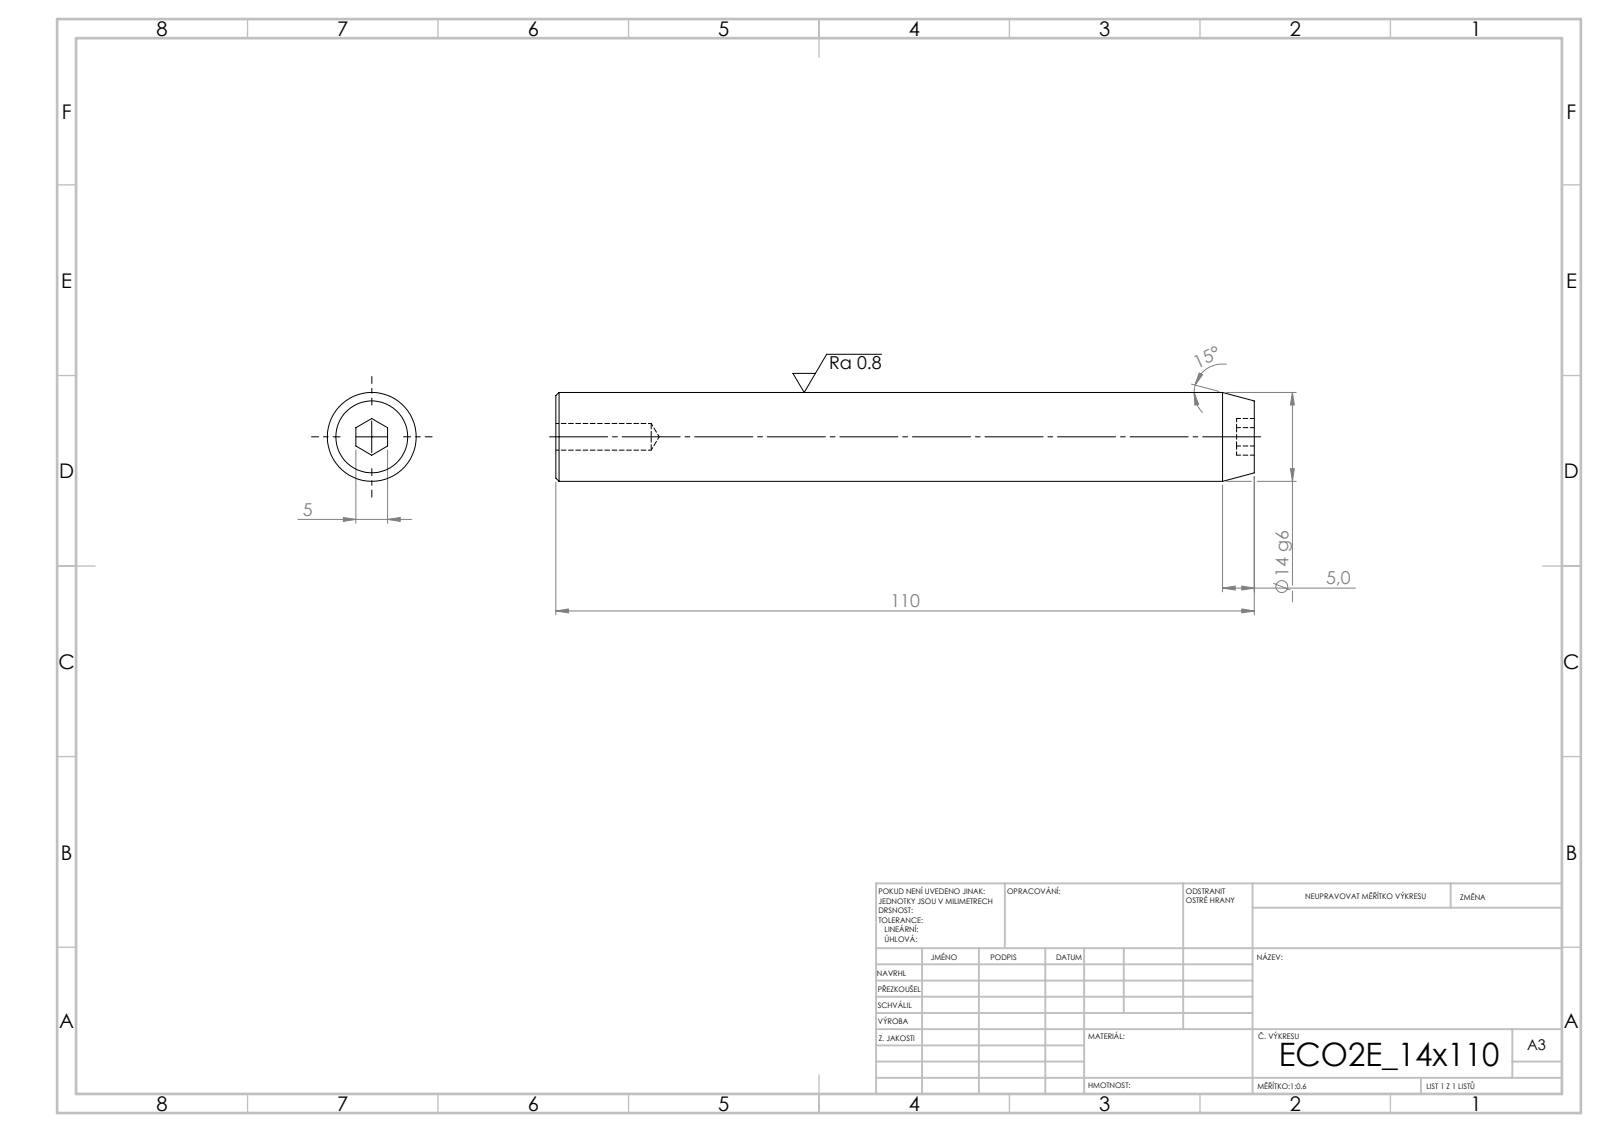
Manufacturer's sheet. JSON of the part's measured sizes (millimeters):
{"step_written_by": "SolidWorks 2019 (CONFIG_CONTROL_DESIGN)", "units": "millimeters", "bodies": {"solids": 1, "faces": 19, "planar": 9, "cylindrical": 4, "other": 6}, "overall_size": [110, 14, 14], "volume_mm3": 16516, "surface_area_mm2": 5314, "round_holes": [[4.2, 1]], "round_bosses_or_shafts": [[14, 1]], "face_to_face_distances": [110, 5, 2.8, 107.2]}
